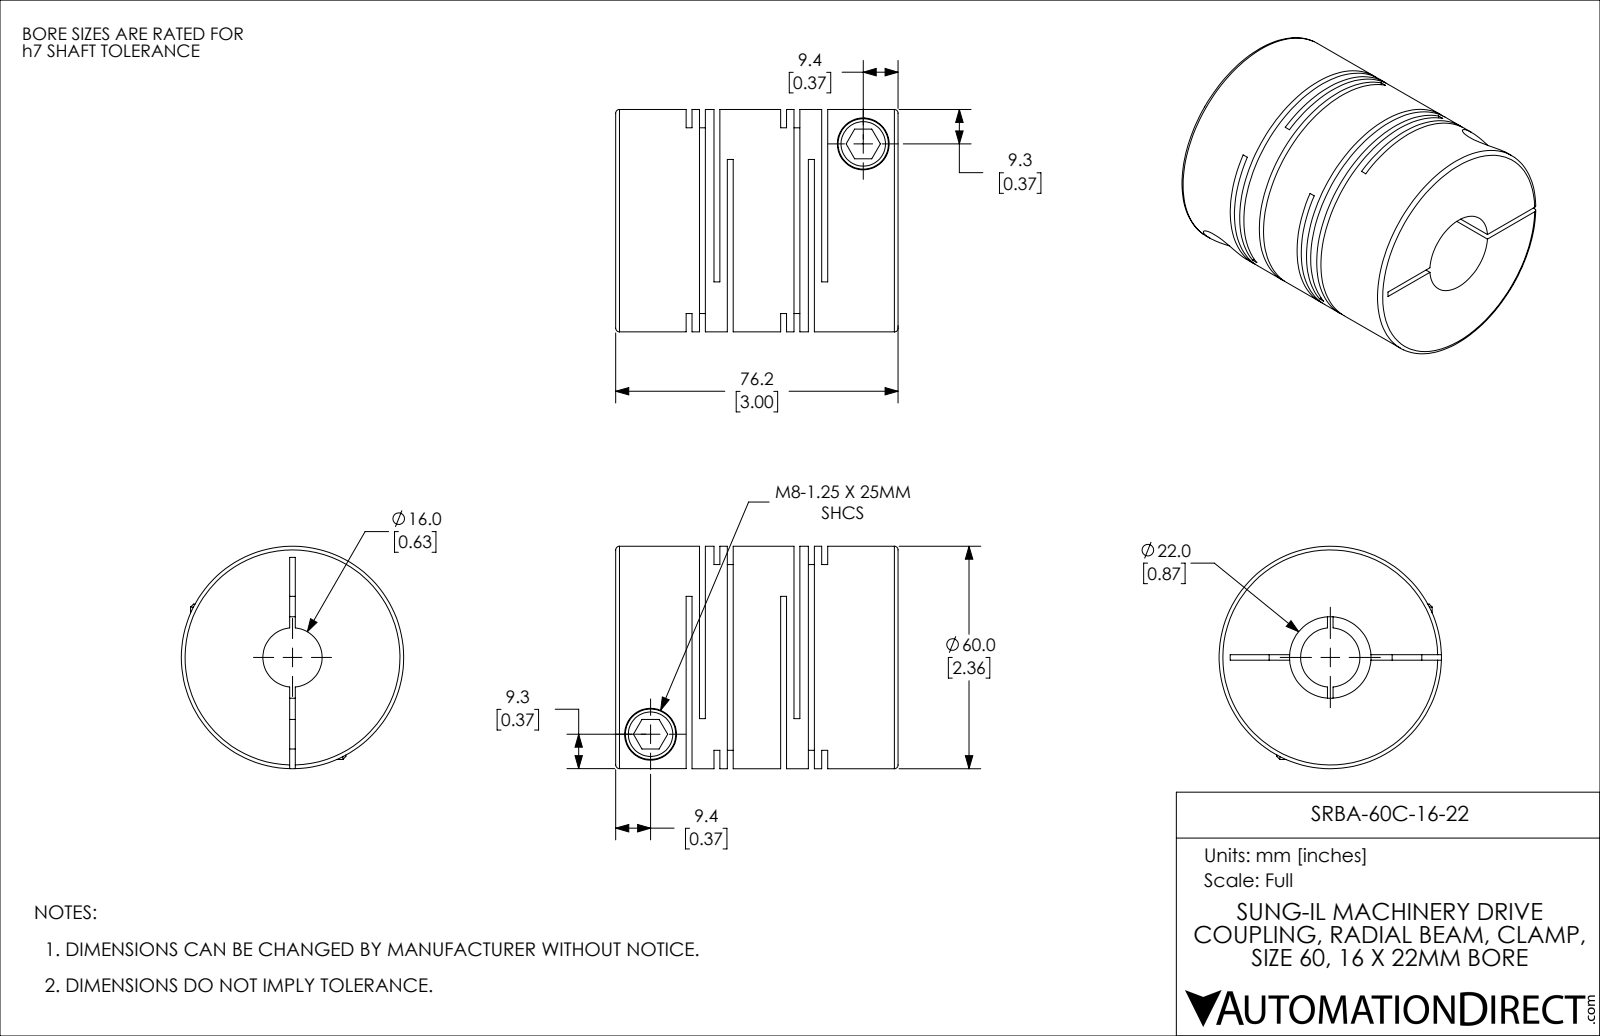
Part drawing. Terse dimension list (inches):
name: SRBA-60C-16-22
written by: SolidWorks 2021 (CONFIG_CONTROL_DESIGN)
unit: in
bodies: 1 solid, 115 faces (60 planar, 42 cylindrical, 13 other)
size: 3 × 2.362 × 2.362
volume: 9.73 in³; area: 90.52 in²
holes: 2× ⌀0.315, 2× ⌀0.551, 1× ⌀0.63, 1× ⌀0.866
bosses: 2× ⌀0.535, 1× ⌀2.362
face distances: 0.063, 0.142, 0.295, 1.004, 1.299, 1.067, 0.709, 0.079, 0.232, 0.941
